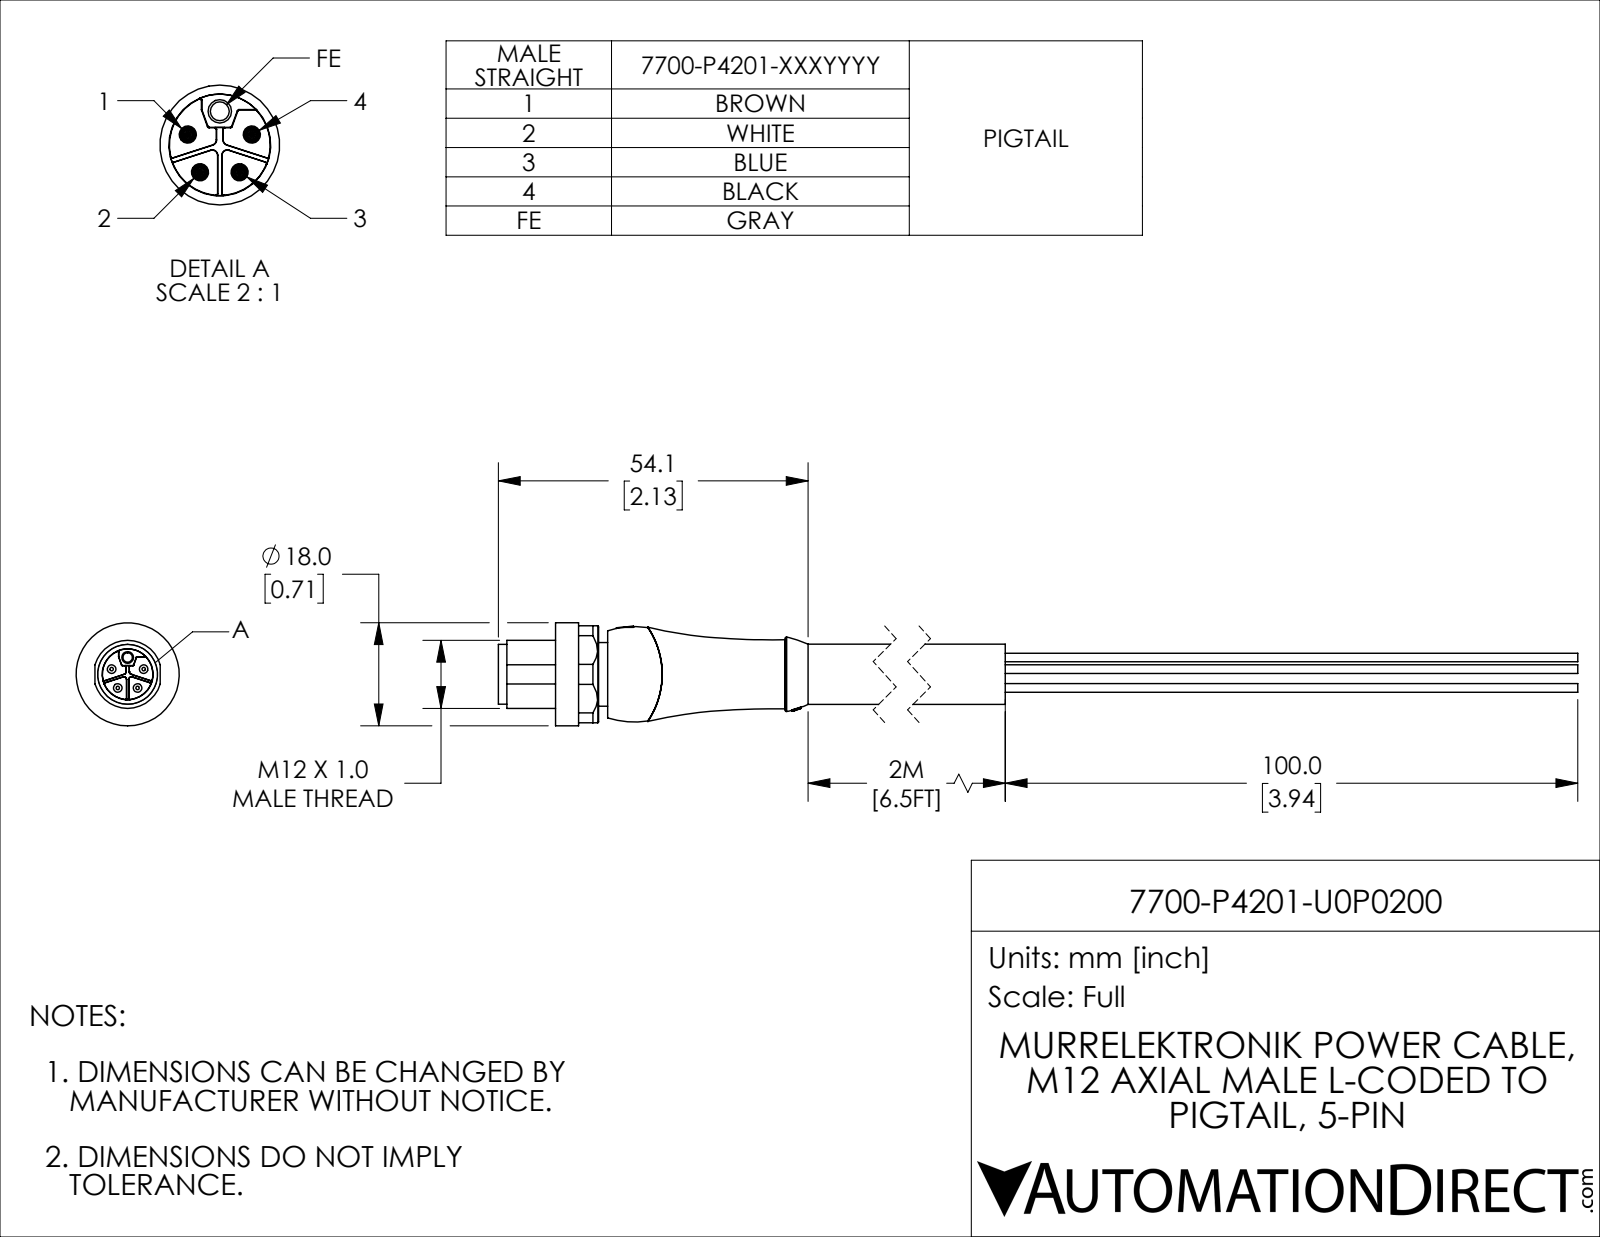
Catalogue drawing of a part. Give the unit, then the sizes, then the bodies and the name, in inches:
Units: inches
Overall size (bounding box): 10.004 × 0.709 × 0.709
Round holes (diameter × count): ⌀0.065 ×1
Round bosses / shafts (diameter × count): ⌀0.059 ×5, ⌀0.709 ×1, ⌀0.468 ×1, ⌀0.437 ×1, ⌀0.413 ×1, ⌀0.411 ×1
Partial cylindrical surfaces — rounded edges, fillets, slot ends (radius × count): R0.006 ×6, R0.044 ×1, R0.352 ×1
Main face-to-face distances: 0.358, 0.075, 0.283, 5.673, 5.39, 5.315, 0.667, 0.047, 0.331, 0.406
Volume: 1.067 in³ · Surface area: 14.12 in²
Bodies: 1 solid, 190 faces (87 planar, 51 cylindrical, 52 other)
Part name (STEP PRODUCT): 7700-P4201-U0P0200
STEP written by: SolidWorks 2021 (CONFIG_CONTROL_DESIGN)
